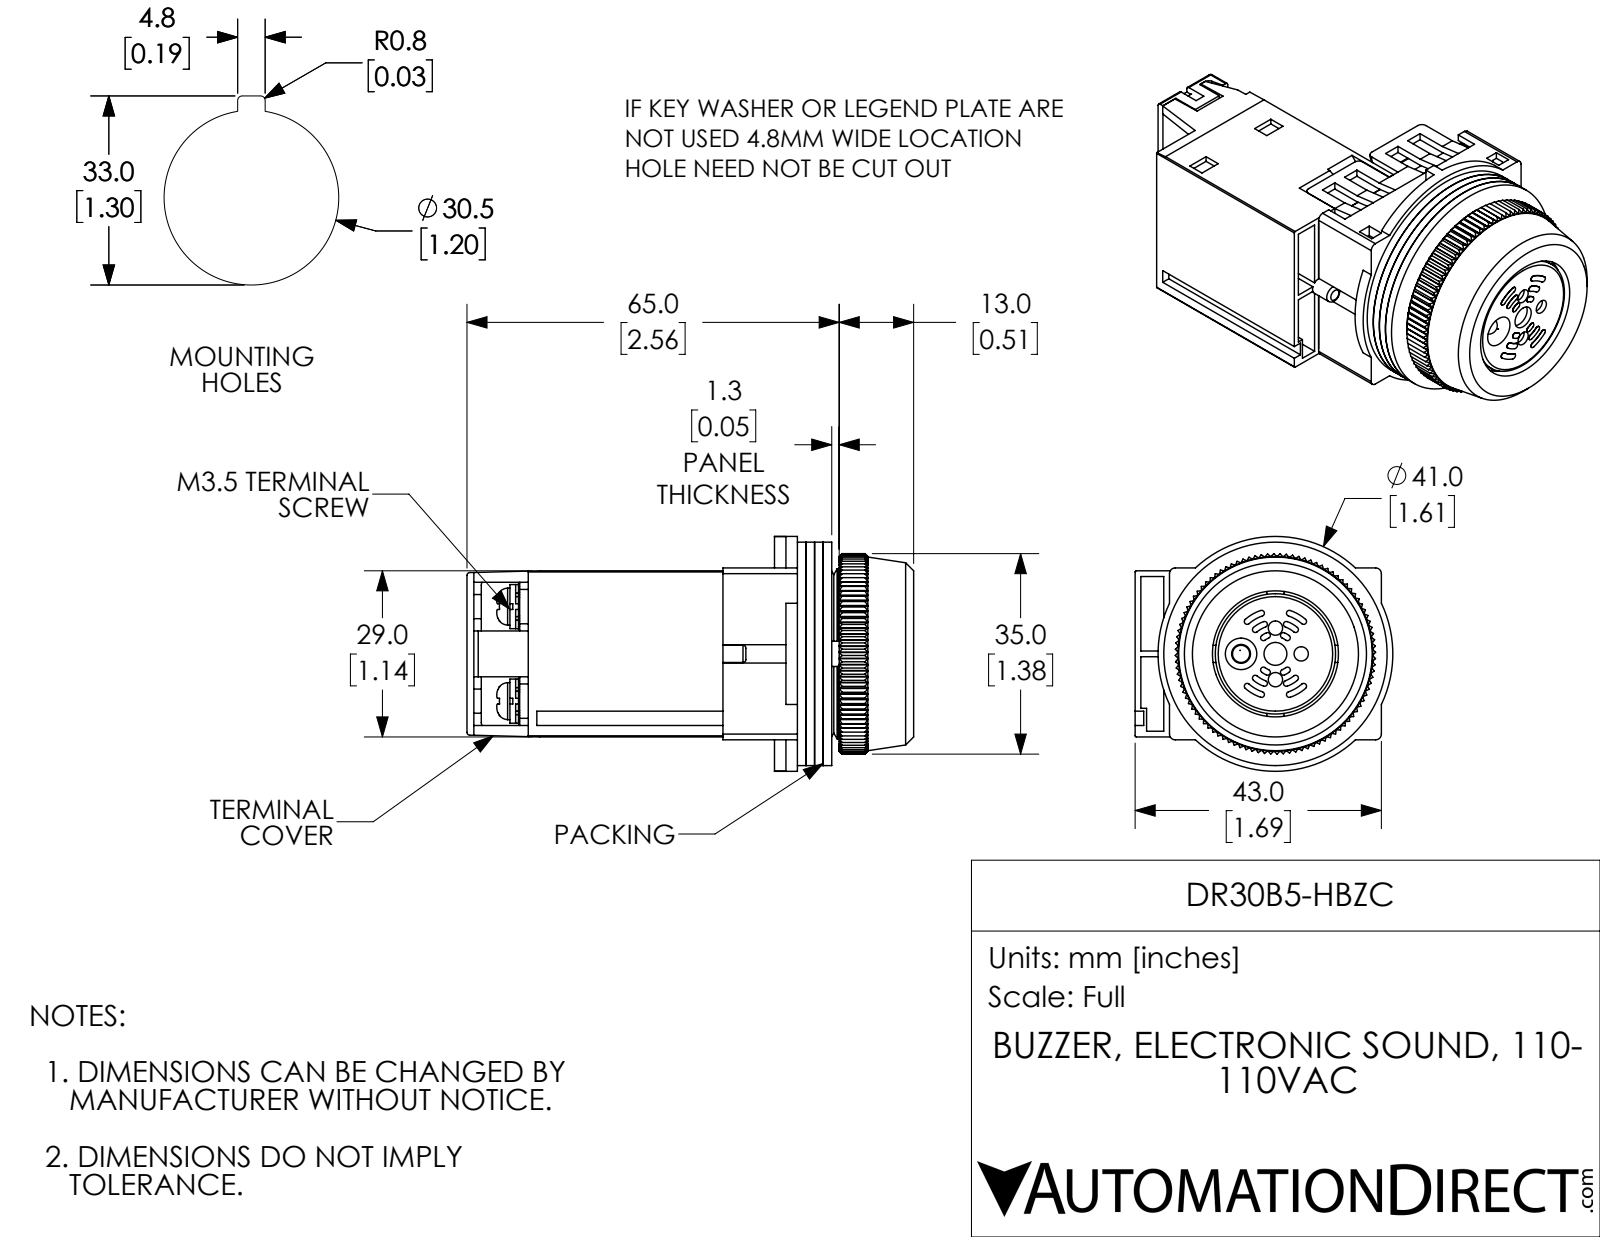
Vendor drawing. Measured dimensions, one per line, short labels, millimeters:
name: DR30B5-HBZC
written by: SolidWorks 2017 (AUTOMOTIVE_DESIGN)
unit: mm
bodies: 16 solids, 1237 faces (817 planar, 332 cylindrical, 88 other)
size: 78 × 45 × 41
volume: 51 440 mm³; area: 29 590 mm²
holes: 3× ⌀2.5, 2× ⌀3, 2× ⌀3.5, 2× ⌀7, 1× ⌀4, 1× ⌀18, 1× ⌀22, 1× ⌀28.3, 1× ⌀29.8
bosses: 2× ⌀3, 1× ⌀41, 1× ⌀39, 1× ⌀30, 1× ⌀30, 1× ⌀28, 1× ⌀21
rounds: 40× R0.5, 12× R1, 8× R1.5, 3× R4, 2× R0.2, 2× R2.5, 1× R0.7, 1× R0.9
face distances: 1.5, 3, 4.5, 2, 17.5, 6, 14.5, 16, 13, 16.5
hole spacings: 16.5, 4.5, 6.2, 6.3, 6.4, 9.7, 9.7, 12.6
